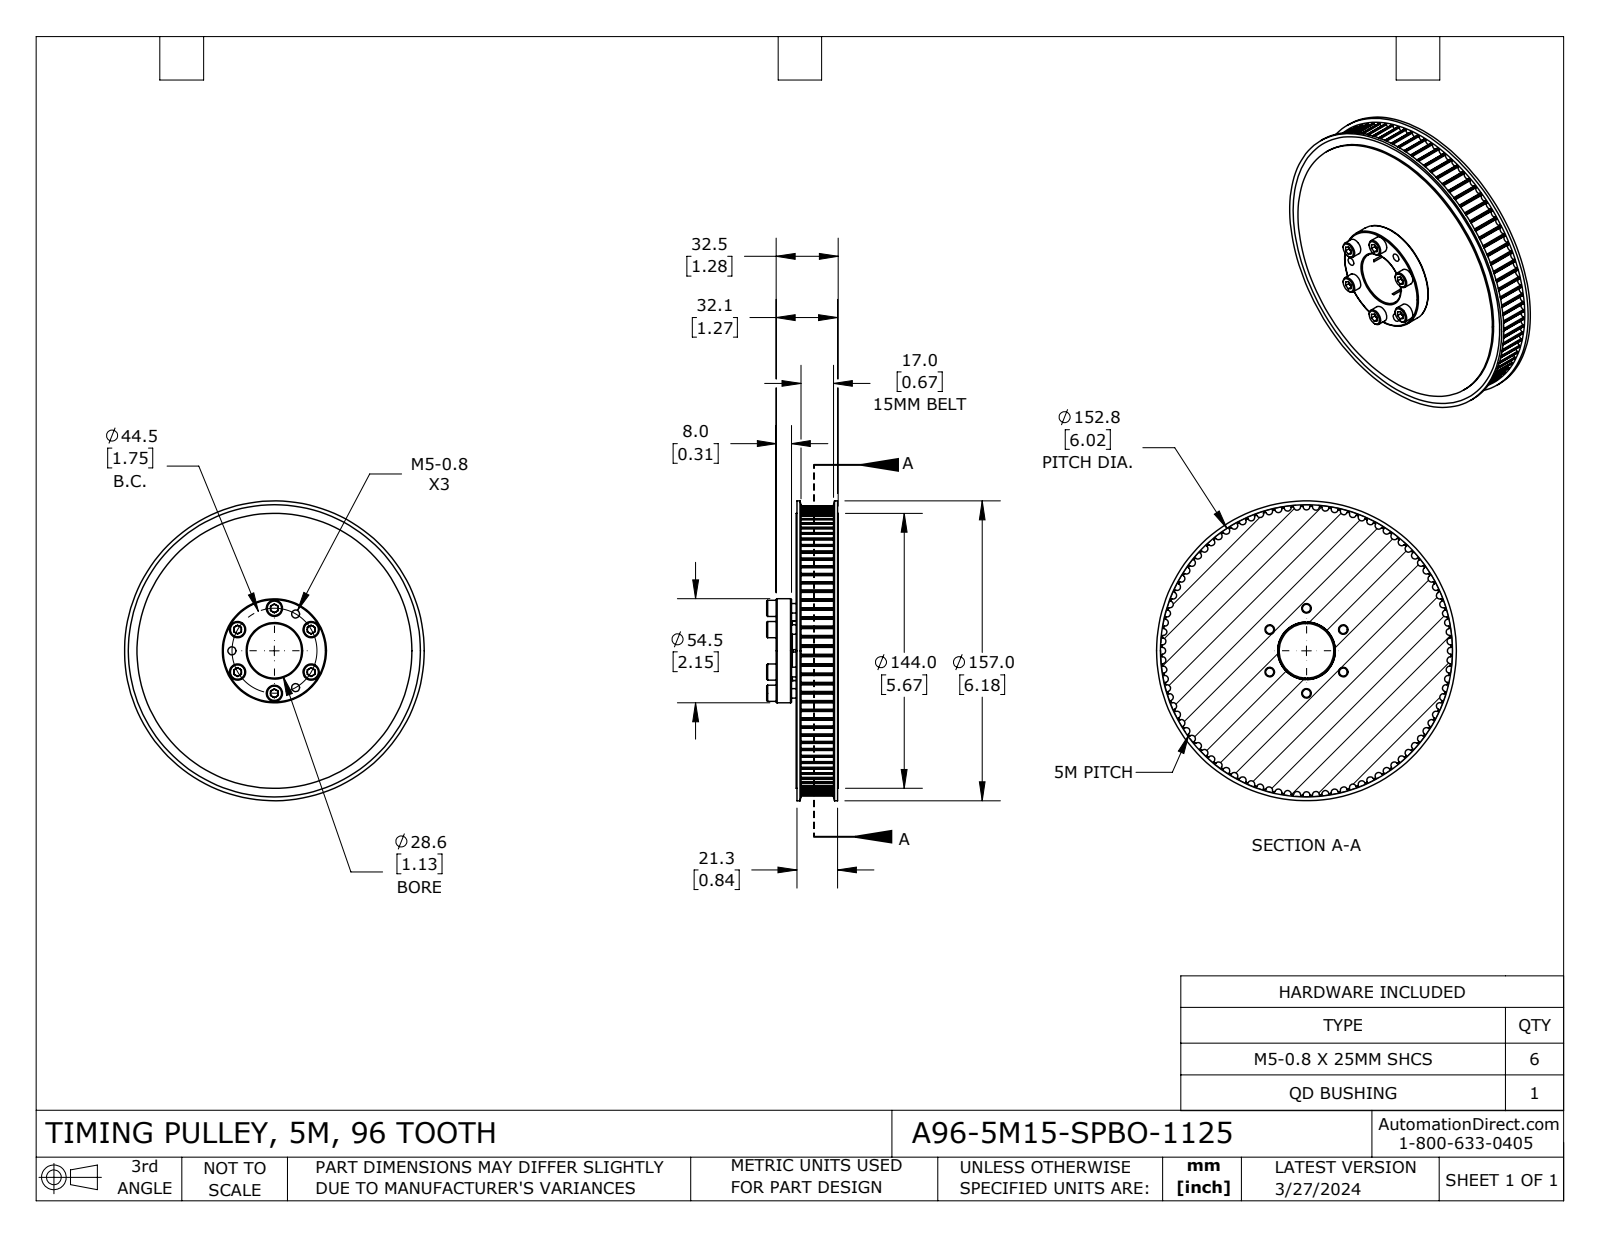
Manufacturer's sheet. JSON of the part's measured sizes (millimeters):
{"part_name": "A96-5M15-SPBO-1125", "step_written_by": "SolidWorks 2021 (CONFIG_CONTROL_DESIGN)", "units": "millimeters", "bodies": {"solids": 10, "faces": 733, "planar": 116, "cylindrical": 555, "other": 62}, "overall_size": [157, 157, 37.5], "volume_mm3": 389261, "surface_area_mm2": 79561, "round_holes": [[4.2, 9], [5.5, 6], [28.57, 1], [28.58, 1], [31.18, 1], [144, 1]], "round_bosses_or_shafts": [[8.5, 6], [5, 6], [157, 1], [54.5, 1], [31.17, 1]], "partial_cylinders_radius": [[0.3, 192], [1.82, 96], [75.83, 1]], "face_to_face_distances": [22, 2.5, 19.5, 0.9, 21.1, 1.6, 18.6, 17, 20.2, 13], "hole_center_spacings": [22.25, 38.54, 11.52, 31.47, 42.99, 38.53, 11.51, 31.46]}
